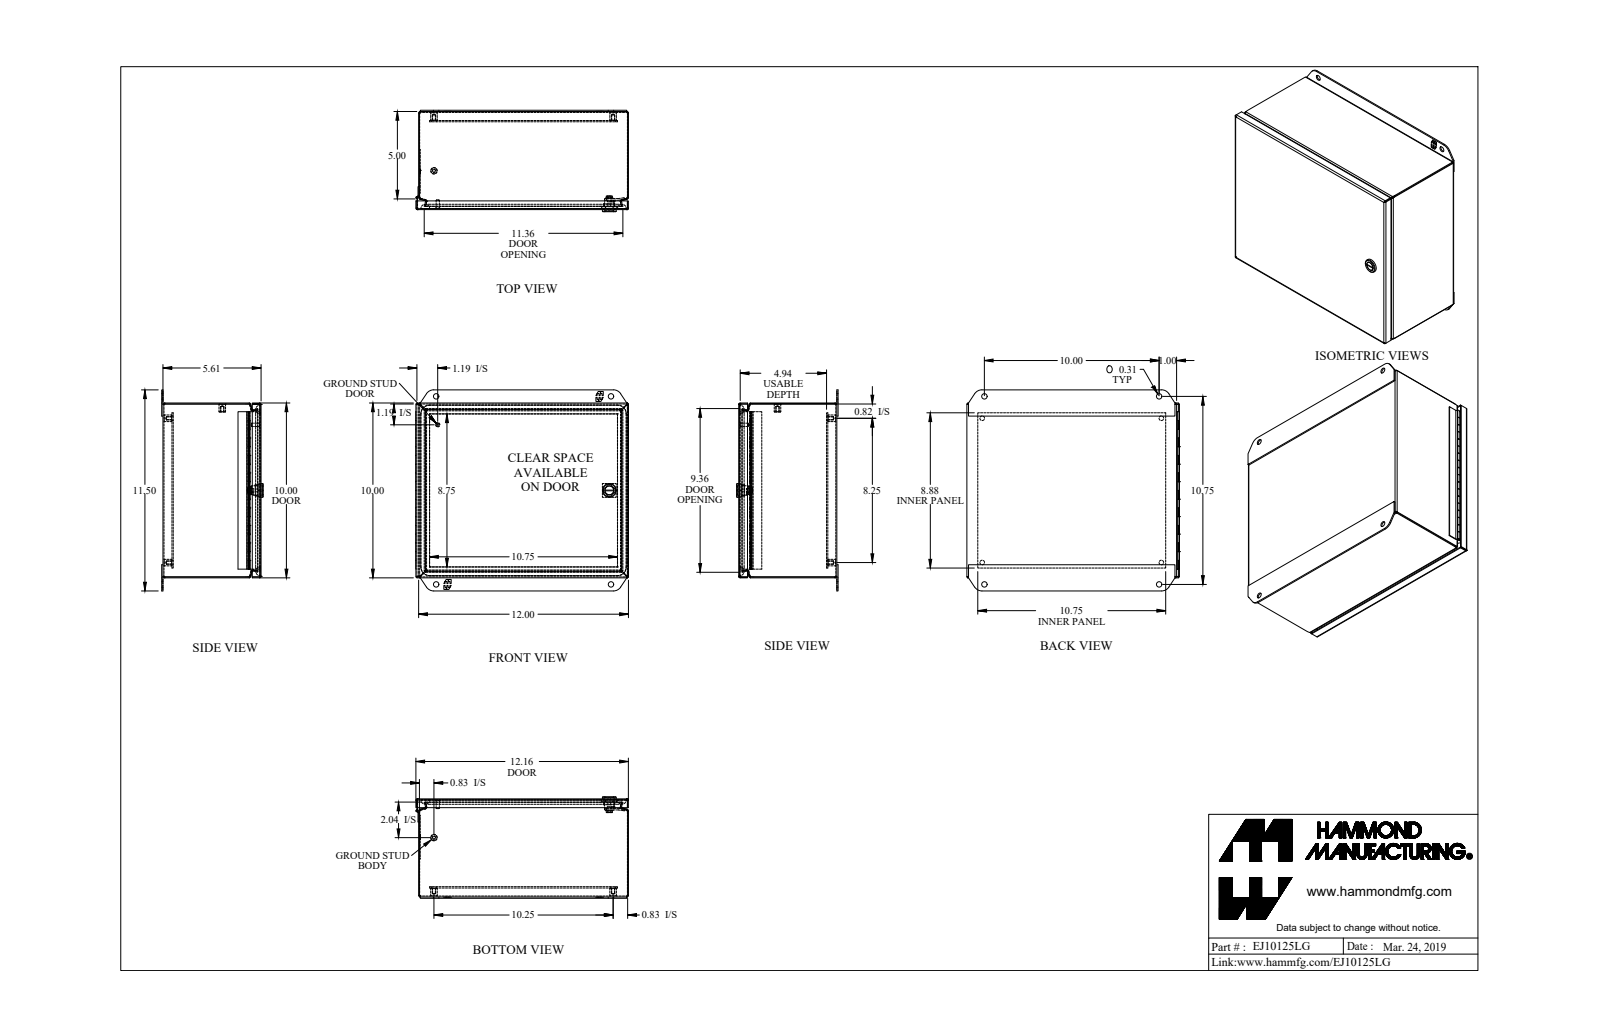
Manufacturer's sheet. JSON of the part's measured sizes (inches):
{"part_name": "EJ10125LG_Default", "step_written_by": "SolidWorks 2019 (CONFIG_CONTROL_DESIGN)", "units": "inches", "bodies": {"solids": 16, "faces": 675, "planar": 377, "cylindrical": 206, "other": 92}, "overall_size": [12.165, 11.5, 5.805], "volume_in3": 42.92, "surface_area_in2": 1411, "round_holes": [[0.156, 5], [0.265, 4], [0.313, 4], [0.05, 1], [0.516, 1]], "round_bosses_or_shafts": [[0.375, 5], [0.788, 1], [0.535, 1], [0.496, 1], [0.435, 1], [0.25, 1], [0.188, 1], [0.1, 1]], "partial_cylinders_radius": [[0.029, 16], [0.086, 16], [0.281, 10], [0.25, 4], [0.499, 4], [0.5, 4], [0.06, 2], [0.539, 2]], "face_to_face_distances": [0.057, 5.554, 0.072, 0.589, 9.943, 5.611, 5.497, 11.943, 0.46, 0.517], "hole_center_spacings": [10.202, 13.158, 13.884, 1.256, 1.257, 4.131, 8.25, 8.25]}
